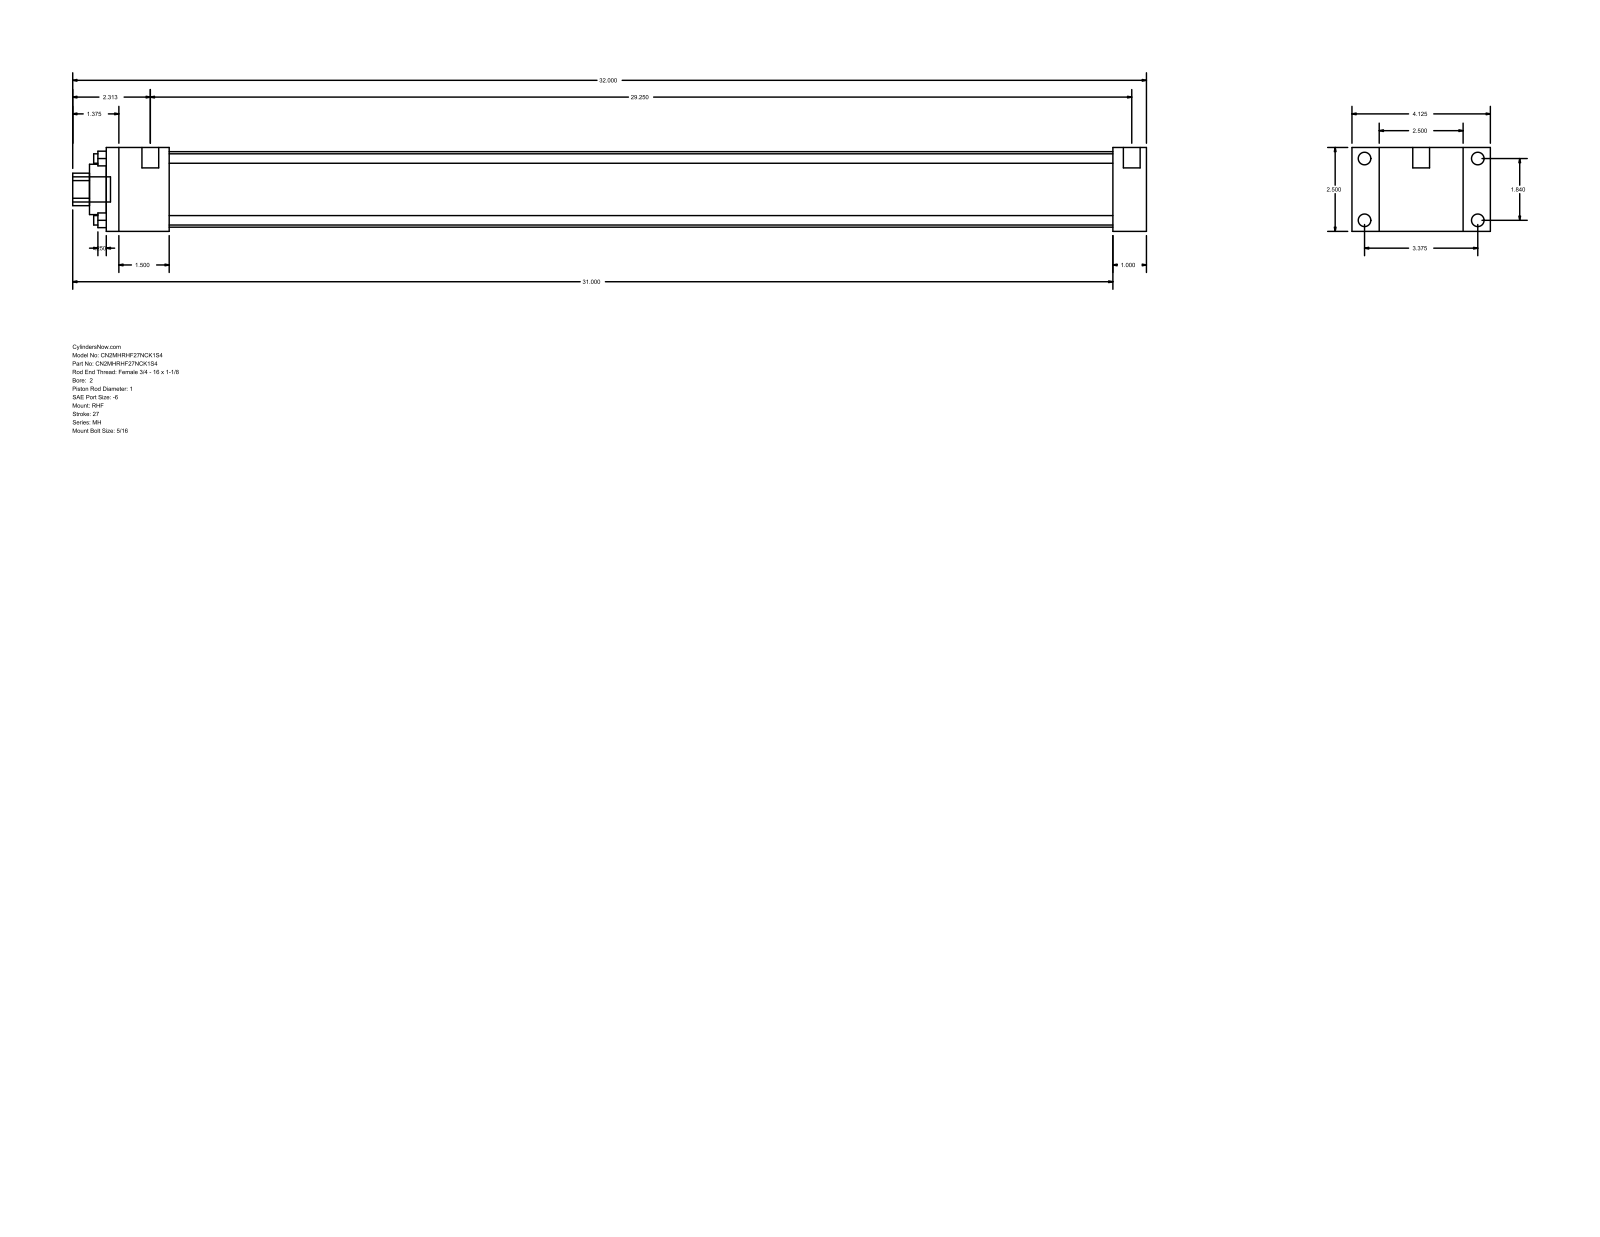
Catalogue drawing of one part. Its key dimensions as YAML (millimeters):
part_name: "MH_RHF__0200_1"
step_written_by: "GSSL Pune (CONFIG_CONTROL_DESIGN)"
units: millimeters
bodies: {solids: 0, faces: 88, planar: 60, cylindrical: 28, other: 0}
overall_size: [812.8, 104.78, 63.5]
round_holes:
  - {diameter: 7.14, count: 4}
  - {diameter: 25.4, count: 1}
  - {diameter: 38.1, count: 1}
  - {diameter: 57.15, count: 1}
round_bosses_or_shafts:
  - {diameter: 9.53, count: 4}
  - {diameter: 5.56, count: 4}
  - {diameter: 12.7, count: 2}
  - {diameter: 19.05, count: 1}
partial_cylinders:
  - {radius: 12.29, count: 1}
face_to_face_distances: [63.5, 25.4, 20.64, 84.14, 787.4, 762, 104.78, 47.63, 714.37, 739.77]
hole_center_spacings: [33.05, 46.74, 66.1]
